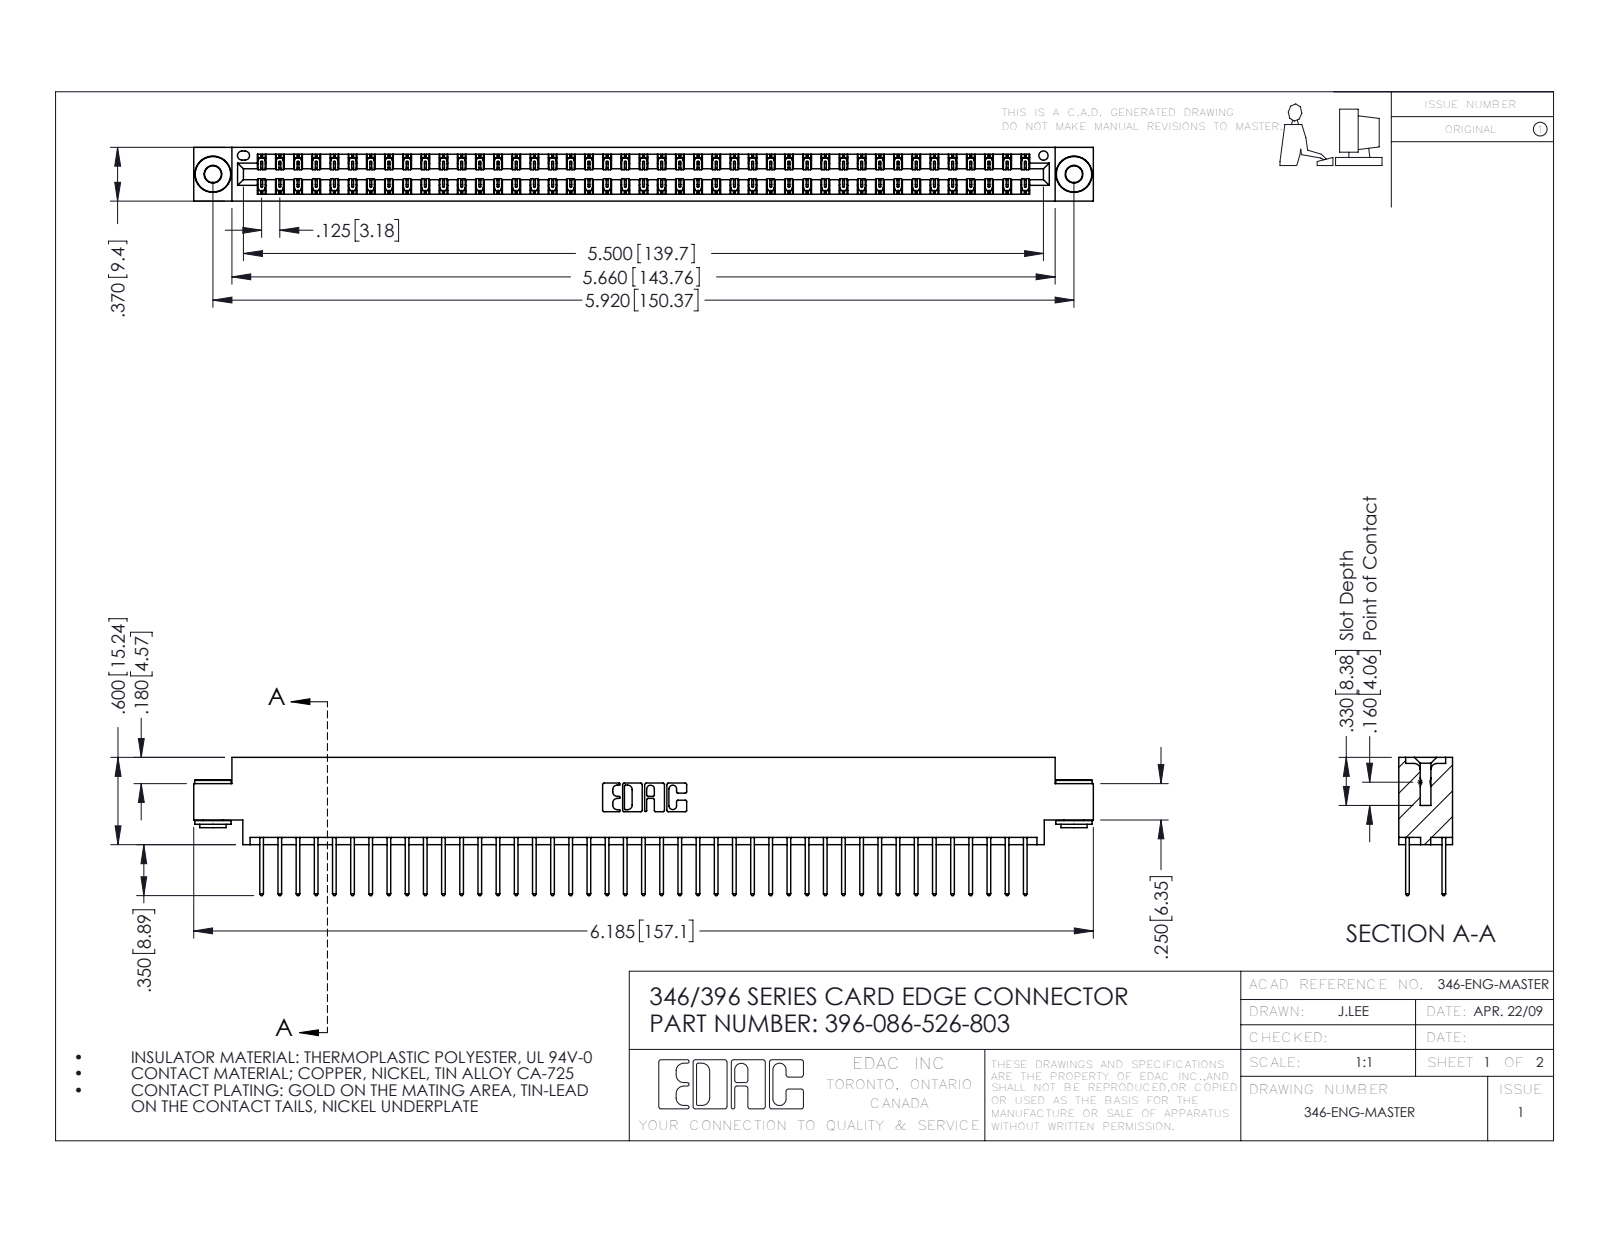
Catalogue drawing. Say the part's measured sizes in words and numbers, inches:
The part is named "345-250-002_345-250-002-102; 396-086-526-803; 345-292-001_345-293-126; 346 Part_0.170 Offset - 0.156 Dia-TH". Its 3-D file was written by "SolidWorks 2016 (CONFIG_CONTROL_DESIGN)". It is 89 solids with 4636 faces: 3100 planar, 1528 cylindrical and 8 other. Overall it measures 6.185 by 0.95 by 0.37 inches. Its volume is 0.936 cubic inches and its surface area 34.28 square inches. Round holes: 2 of diameter 0.116, 2 of diameter 0.156, 1 of diameter 0.064. Round bosses or shafts: 2 of diameter 0.25, 2 of diameter 0.18, 2 of diameter 0.136. Partial cylindrical surfaces (rounded edges, fillets, slot ends): 129 of radius 0.006, 86 of radius 0.01, 22 of radius 0.01, 6 of radius 0.007, 6 of radius 0.031, 3 of radius 0.026, 2 of radius 0.014, 2 of radius 0.022. The main face-to-face distances are 0.048, 0.322, 0.25, 0.37, 0.025, 0.072, 0.298, 0.275, 0.148, 0.222. The hole center spacings are 0.246, 5.711, 5.92.
